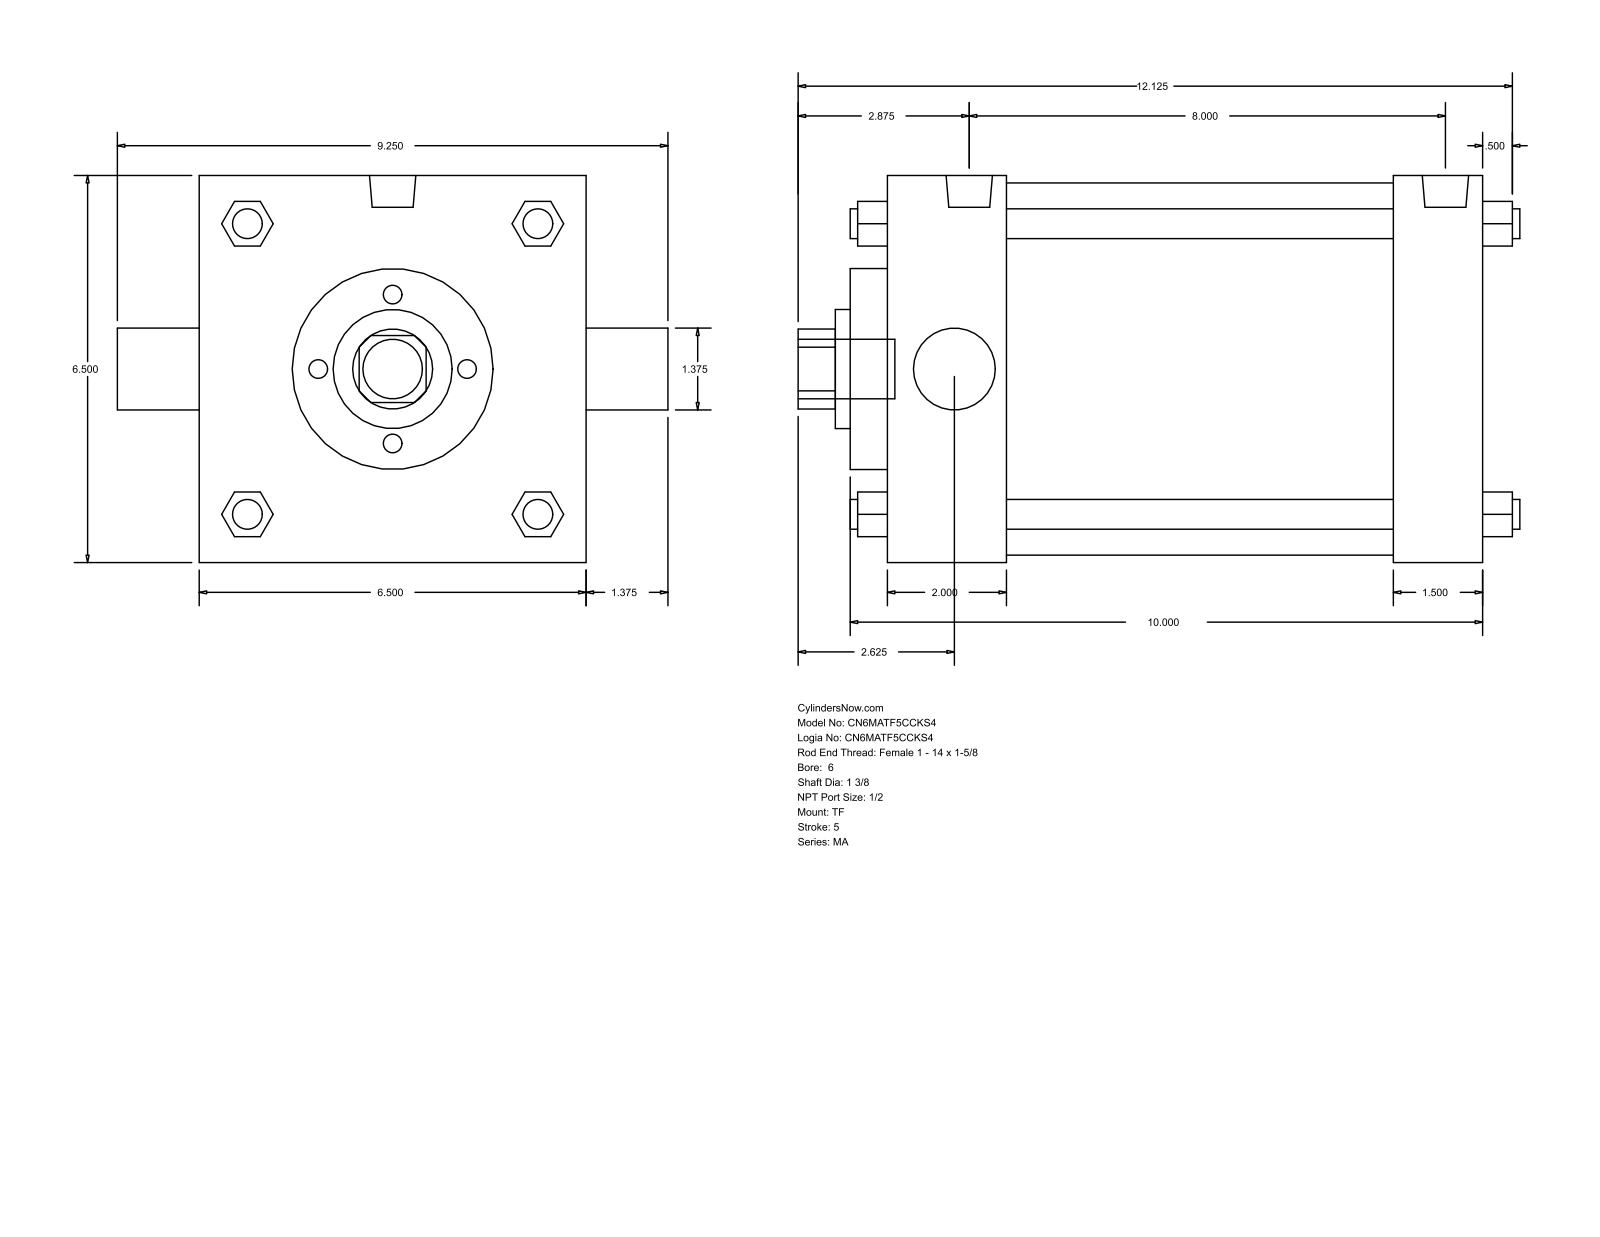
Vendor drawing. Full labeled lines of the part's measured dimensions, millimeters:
Part name (STEP PRODUCT): MA_TF__0600_1.375
STEP written by: GSSL Pune (CONFIG_CONTROL_DESIGN)
Units: millimetres
Bodies: 0 solids, 122 faces (93 planar, 29 cylindrical, 0 other)
Overall size (bounding box): 307.98 × 234.95 × 165.1
Round holes (diameter × count): ⌀34.92 ×2, ⌀50.8 ×1, ⌀85.72 ×1, ⌀158.75 ×1
Round bosses / shafts (diameter × count): ⌀12.7 ×4, ⌀17.46 ×3, ⌀19.77 ×2, ⌀25.4 ×1
Partial cylindrical surfaces — rounded edges, fillets, slot ends (radius × count): R17.06 ×1
Main face-to-face distances: 165.1, 257.17, 50.8, 219.08, 206.37, 168.28, 38.09, 15.87, 66.67, 234.95
